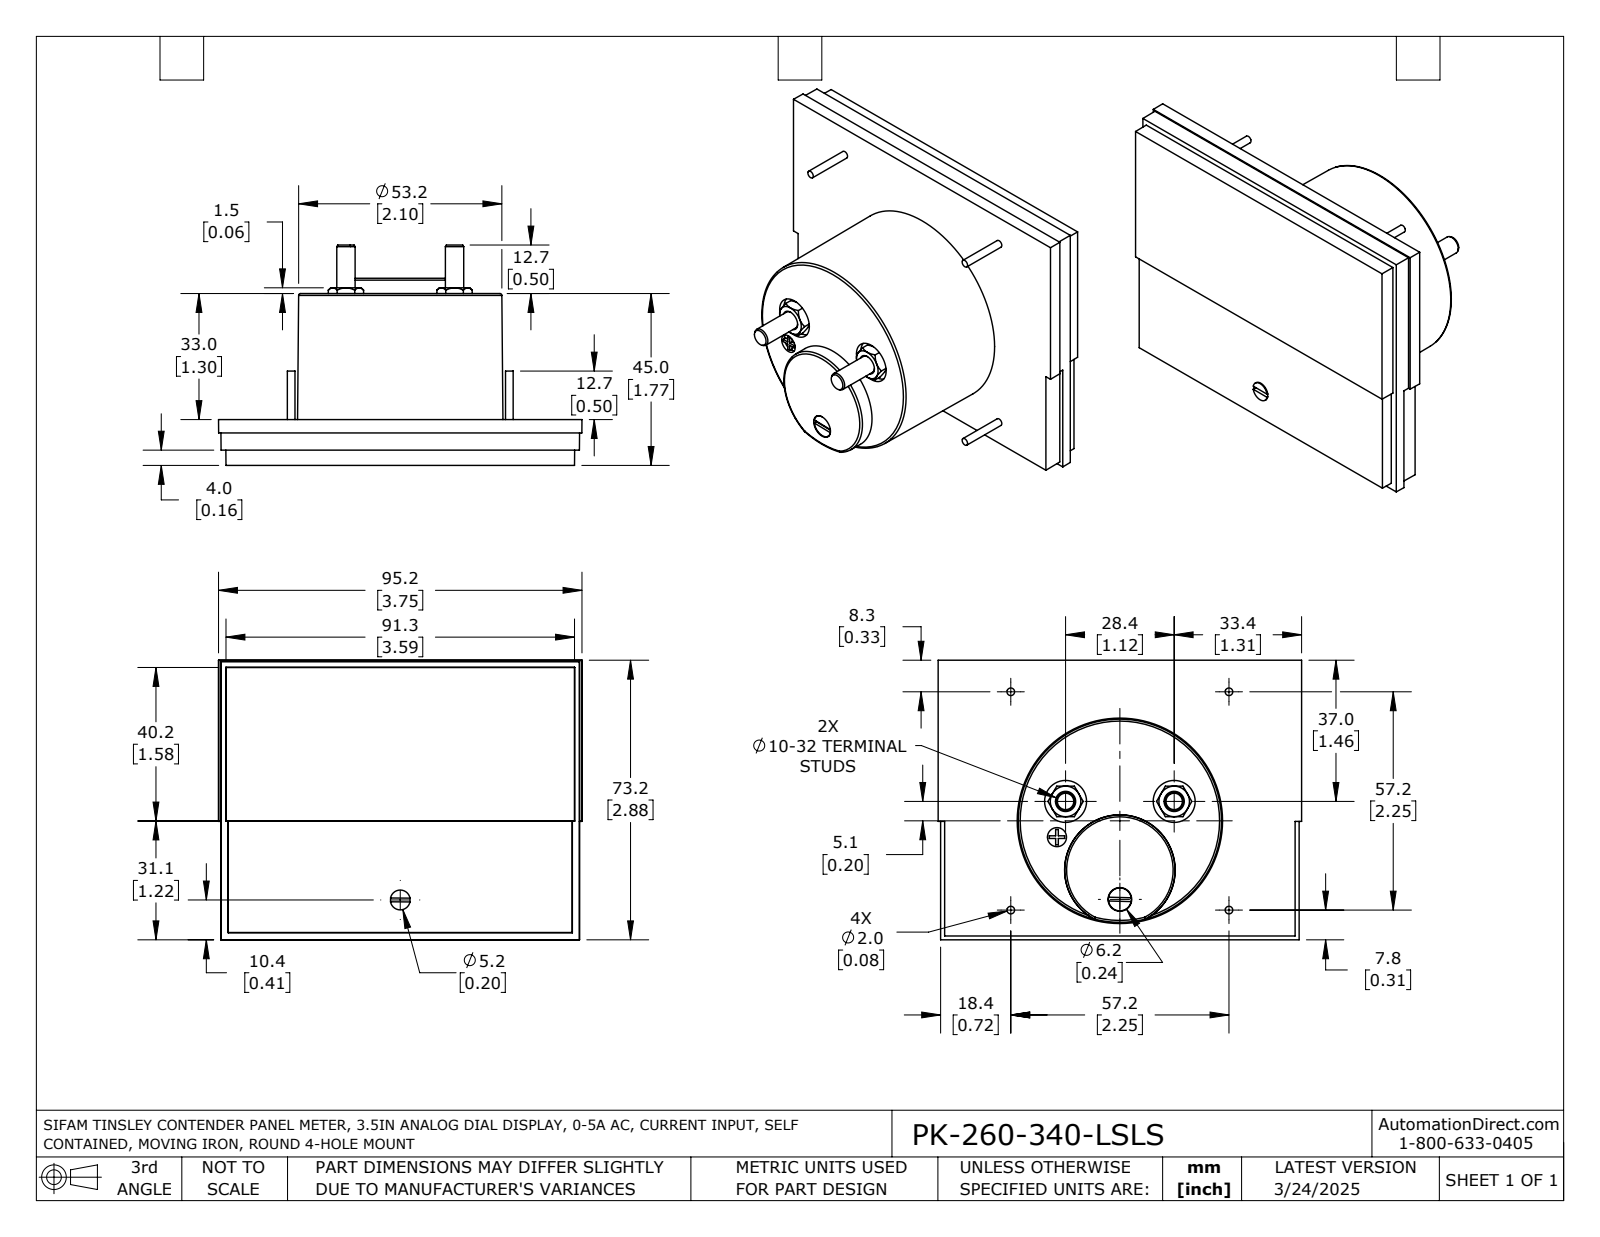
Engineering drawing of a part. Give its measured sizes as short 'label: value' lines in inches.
name: PK-260-340-LSLS
written by: SolidWorks 2021 (AUTOMOTIVE_DESIGN)
unit: in
bodies: 1 solid, 163 faces (76 planar, 31 cylindrical, 56 other)
size: 3.748 × 2.882 × 2.272
volume: 9.446 in³; area: 38.39 in²
holes: 2× ⌀0.433, 1× ⌀0.197, 1× ⌀0.244
bosses: 4× ⌀0.079, 2× ⌀0.189, 1× ⌀0.236, 1× ⌀0.205
rounds: 1× R0.1
face distances: 0.472, 0.03, 0.443, 1.772, 1.299, 1.742, 0.157, 0.073, 0.315, 1.457
hole spacings: 1.155, 0.379, 0.912, 1.12, 1.263
